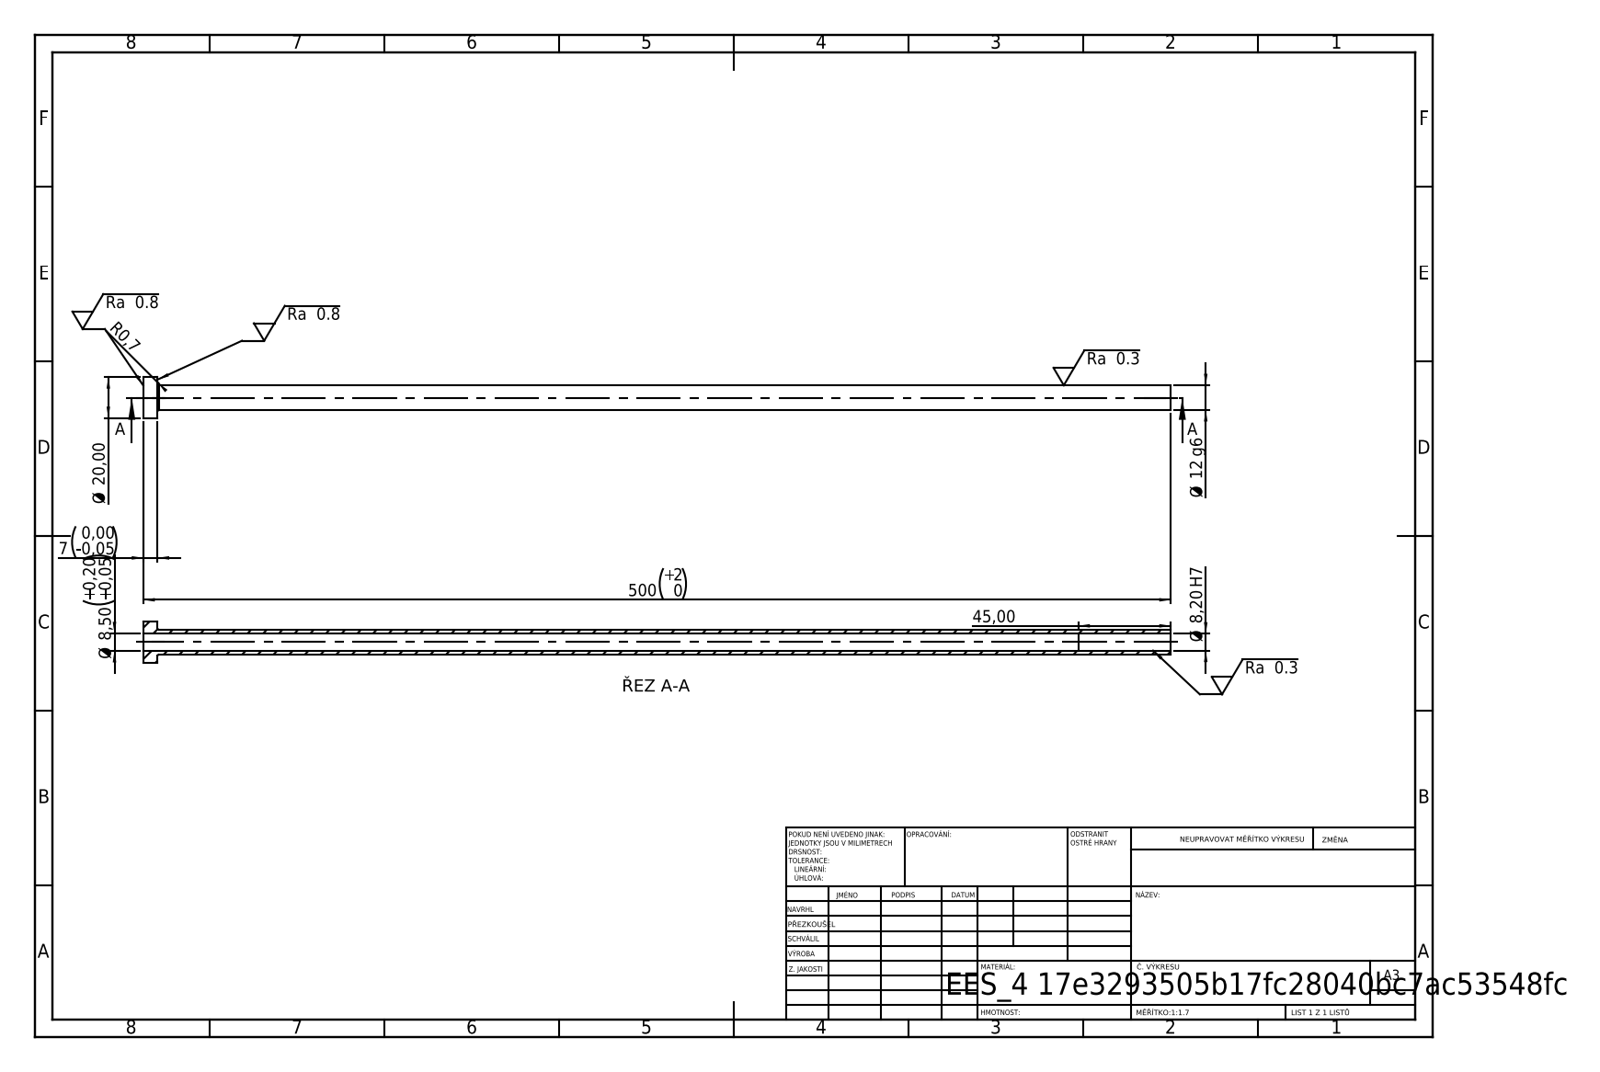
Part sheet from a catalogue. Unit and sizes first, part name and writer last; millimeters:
Units: millimetres
Overall size (bounding box): 500 × 20 × 20
Round holes (diameter × count): ⌀8.2 ×1, ⌀8.5 ×1
Round bosses / shafts (diameter × count): ⌀20 ×1, ⌀12 ×1
Main face-to-face distances: 7, 500, 493, 455, 448, 45
Volume: 29 765 mm³ · Surface area: 32 846 mm²
Bodies: 1 solid, 14 faces (4 planar, 8 cylindrical, 2 other)
STEP written by: SolidWorks 2019 (CONFIG_CONTROL_DESIGN)
